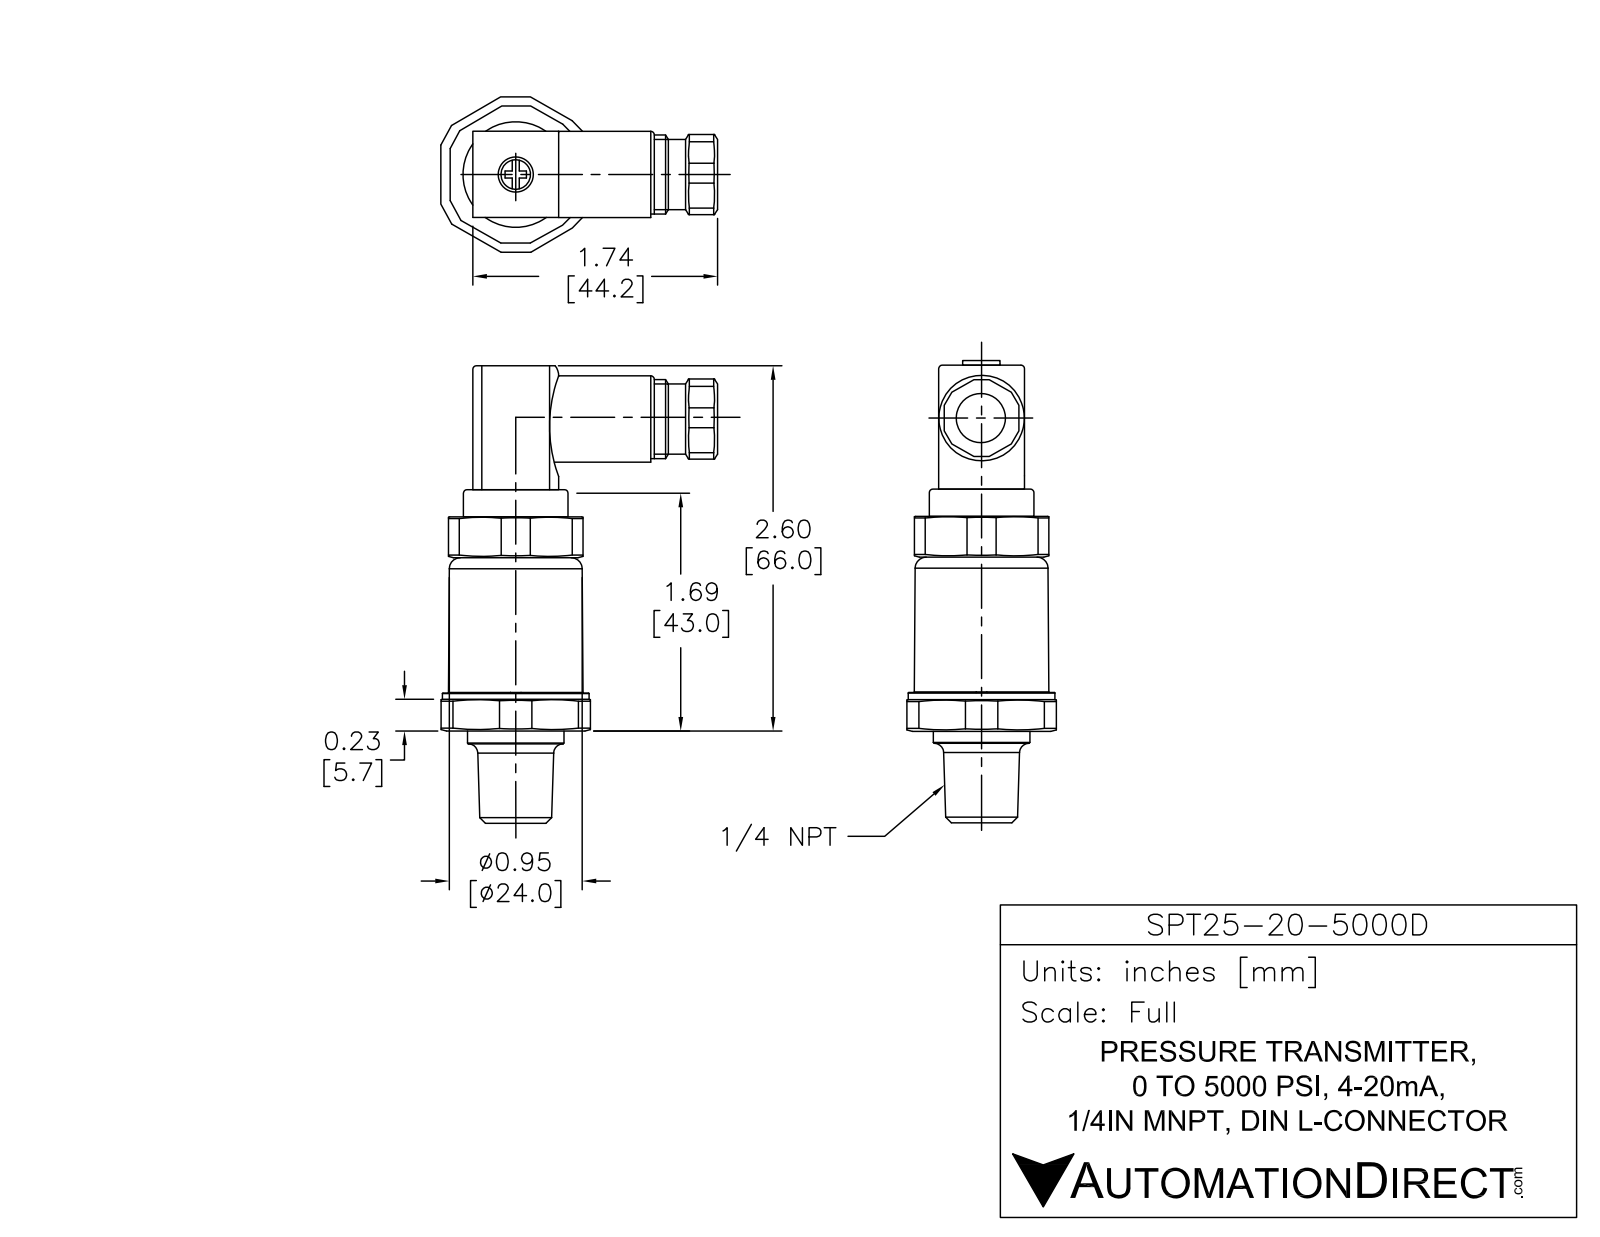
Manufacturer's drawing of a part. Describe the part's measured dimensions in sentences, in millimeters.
The part is named "SPT25-20-5000D". Its 3-D file was written by "SolidWorks 2011 (AUTOMOTIVE_DESIGN)". It is 5 solids with 170 faces: 96 planar, 64 cylindrical and 10 other. Overall it measures 81.25 by 38.01 by 35.71 millimeters. Its volume is 27 900 cubic millimeters and its surface area 10 134 square millimeters. Round holes: 1 of diameter 1, 1 of diameter 3.3, 1 of diameter 7, 1 of diameter 8. Round bosses or shafts: 1 of diameter 26.75, 1 of diameter 24, 1 of diameter 17.5, 1 of diameter 15, 1 of diameter 14, 1 of diameter 11. Partial cylindrical surfaces (rounded edges, fillets, slot ends): 8 of radius 1.5, 4 of radius 1.15, 4 of radius 2.25, 3 of radius 2, 1 of radius 1.15, 1 of radius 1.17, 1 of radius 14.5. The main face-to-face distances are 1.5, 29.5, 31, 15.75, 0.35, 15.4, 6.75, 37.75, 36.25, 5. The hole center spacings are 1.33.
